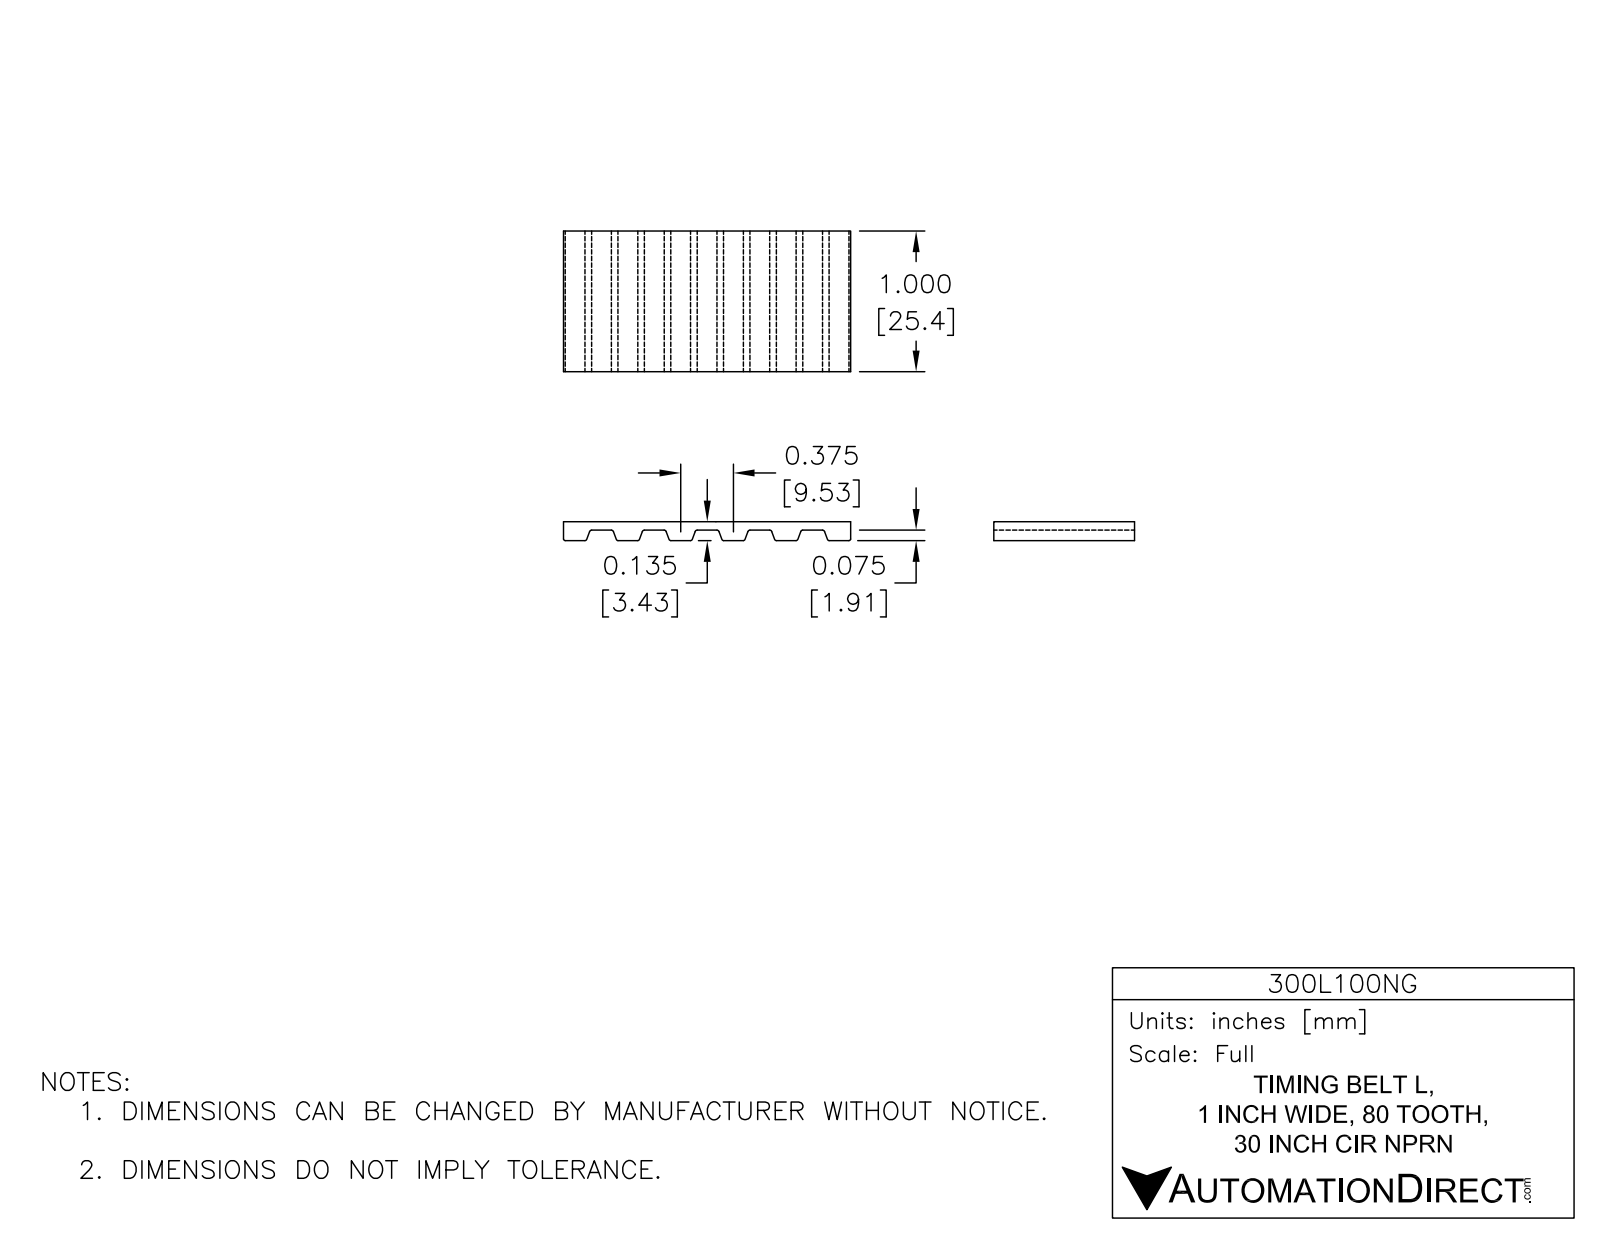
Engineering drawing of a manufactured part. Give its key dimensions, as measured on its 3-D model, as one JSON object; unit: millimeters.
{"part_name": "300L100NG", "step_written_by": "SolidWorks 2014 (AUTOMOTIVE_DESIGN)", "units": "millimeters", "bodies": {"solids": 1, "faces": 655, "planar": 297, "cylindrical": 358, "other": 0}, "overall_size": [337.5, 76.2, 25.4], "volume_mm3": 44440, "surface_area_mm2": 46560, "partial_cylinders_radius": [[0.5, 316], [36.4, 2], [38.1, 2]], "face_to_face_distances": [1.7, 74.5, 76.2, 72.9, 3.6, 72.6, 1.9, 71, 25.4, 69.1]}
